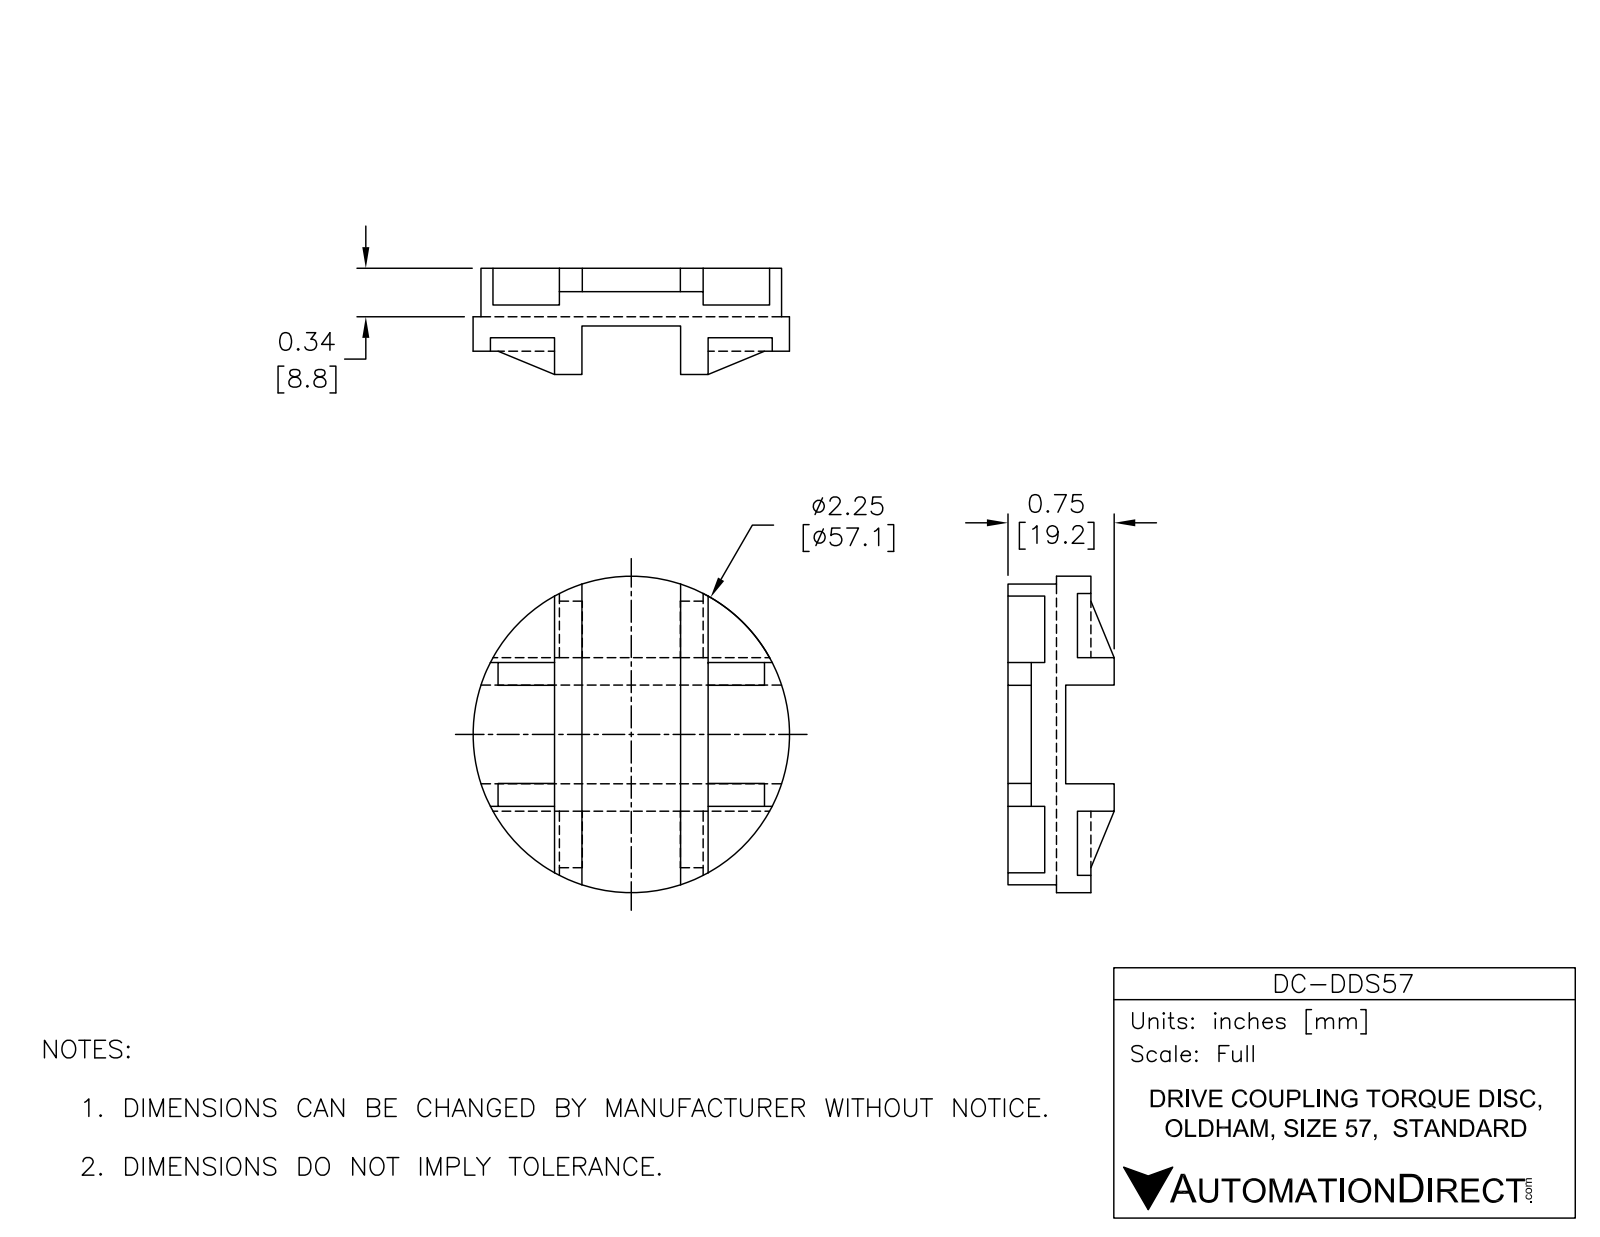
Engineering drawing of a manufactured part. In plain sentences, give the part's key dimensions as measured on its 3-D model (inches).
The part is named "DC-DDS57". Its 3-D file was written by "SolidWorks 2015 (AUTOMOTIVE_DESIGN)". It is 1 solid with 60 faces: 58 planar, 2 cylindrical and 0 other. Overall it measures 2.248 by 2.248 by 0.755 inches. Its volume is 1.336 cubic inches and its surface area 15.51 square inches. Round bosses or shafts: 1 of diameter 2.248. The main face-to-face distances are 0.179, 0.244, 0.166, 0.345, 0.41, 0.589, 0.065, 0.701, 0.195, 0.896.
